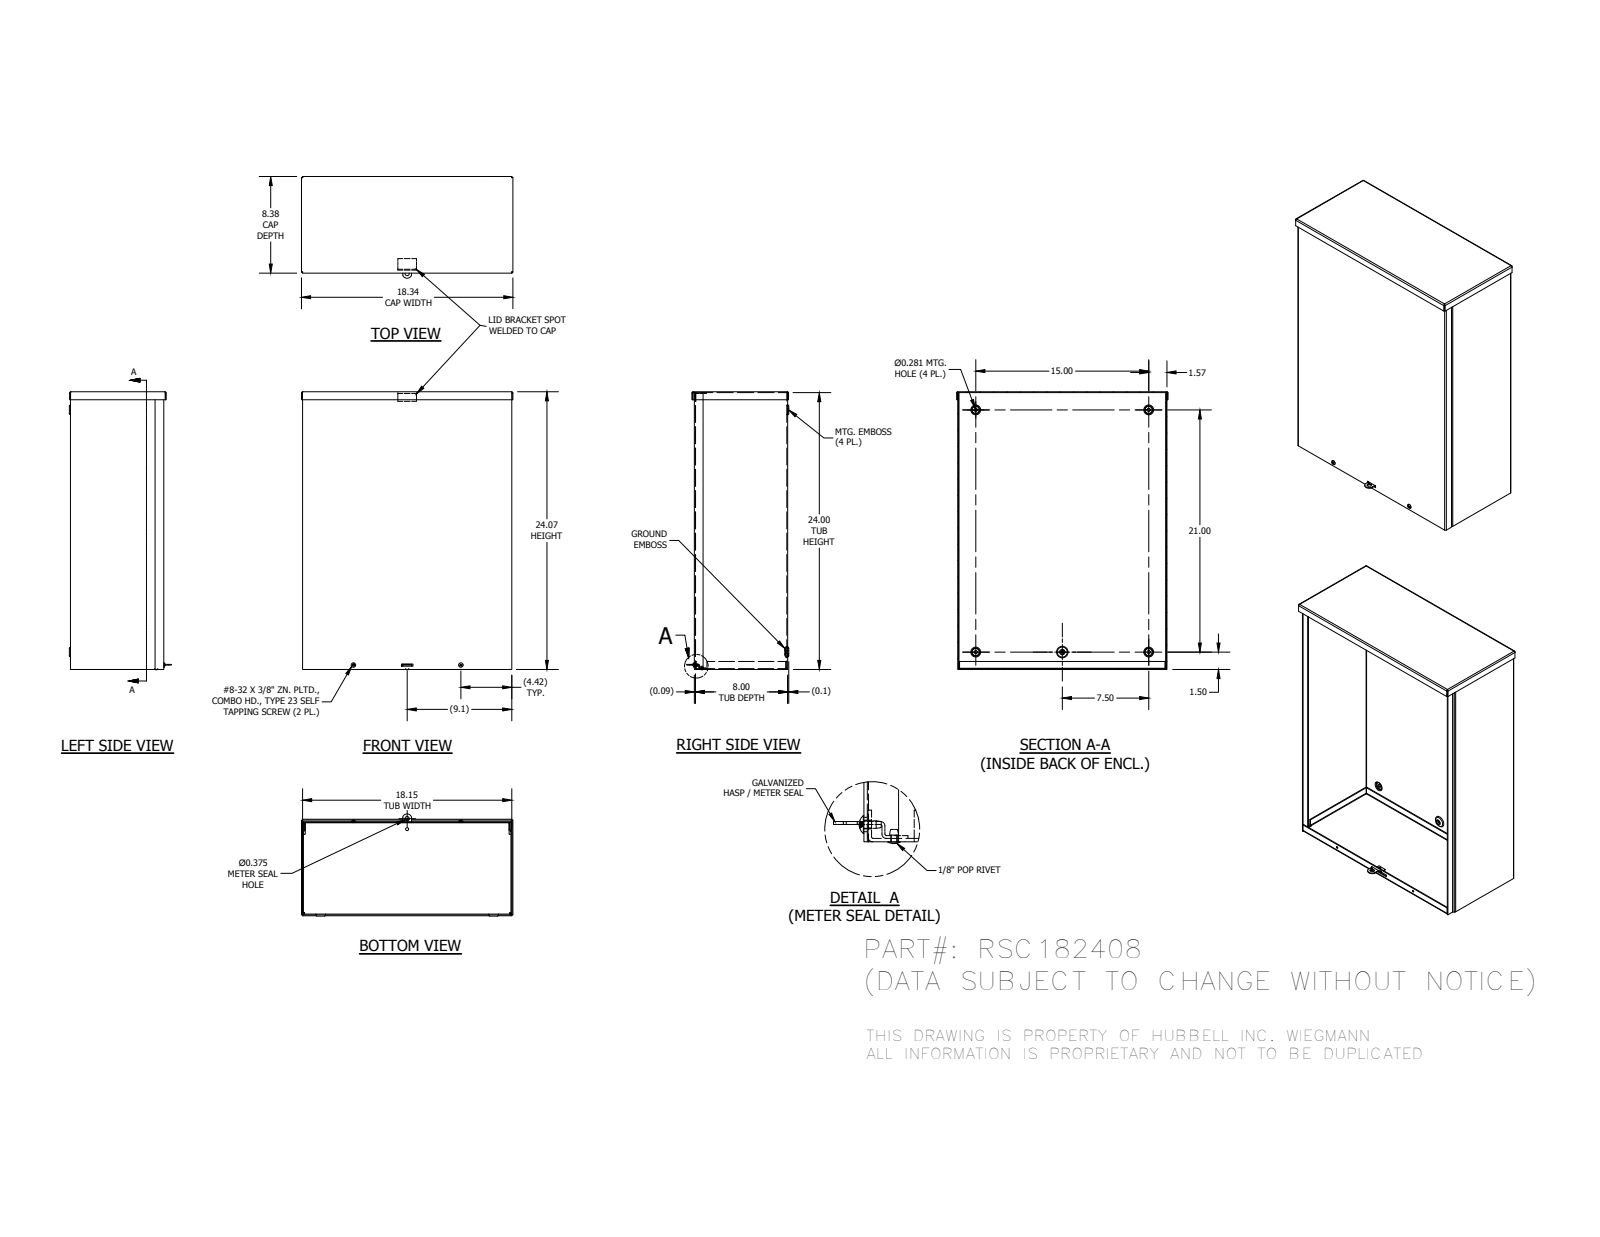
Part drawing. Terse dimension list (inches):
name: RSC182408BKPA; RSC1808EWPA-14GA; RSC1824LFA; RSC1808CPA-14GA (+5 more)
written by: Autodesk Inventor 2014 (AUTOMOTIVE_DESIGN)
unit: in
bodies: 9 solids, 320 faces (183 planar, 61 cylindrical, 76 other)
size: 24.114 × 18.335 × 8.85
volume: 121.6 in³; area: 3 312 in²
holes: 4× ⌀0.281, 4× ⌀0.313, 2× ⌀0.147, 1× ⌀0.125, 1× ⌀0.136, 1× ⌀0.171, 1× ⌀0.375
bosses: 2× ⌀0.384, 2× ⌀0.164, 1× ⌀0.262, 1× ⌀0.233, 1× ⌀0.125
rounds: 19× R0.031, 17× R0.105, 2× R0.093, 1× R0.4
face distances: 0.074, 8.016, 8.09, 7.942, 18.074, 24, 18, 18.148, 24.074, 23.926
hole spacings: 3.058, 12.208, 4.79, 7.5, 9.313, 15, 21, 22.299
